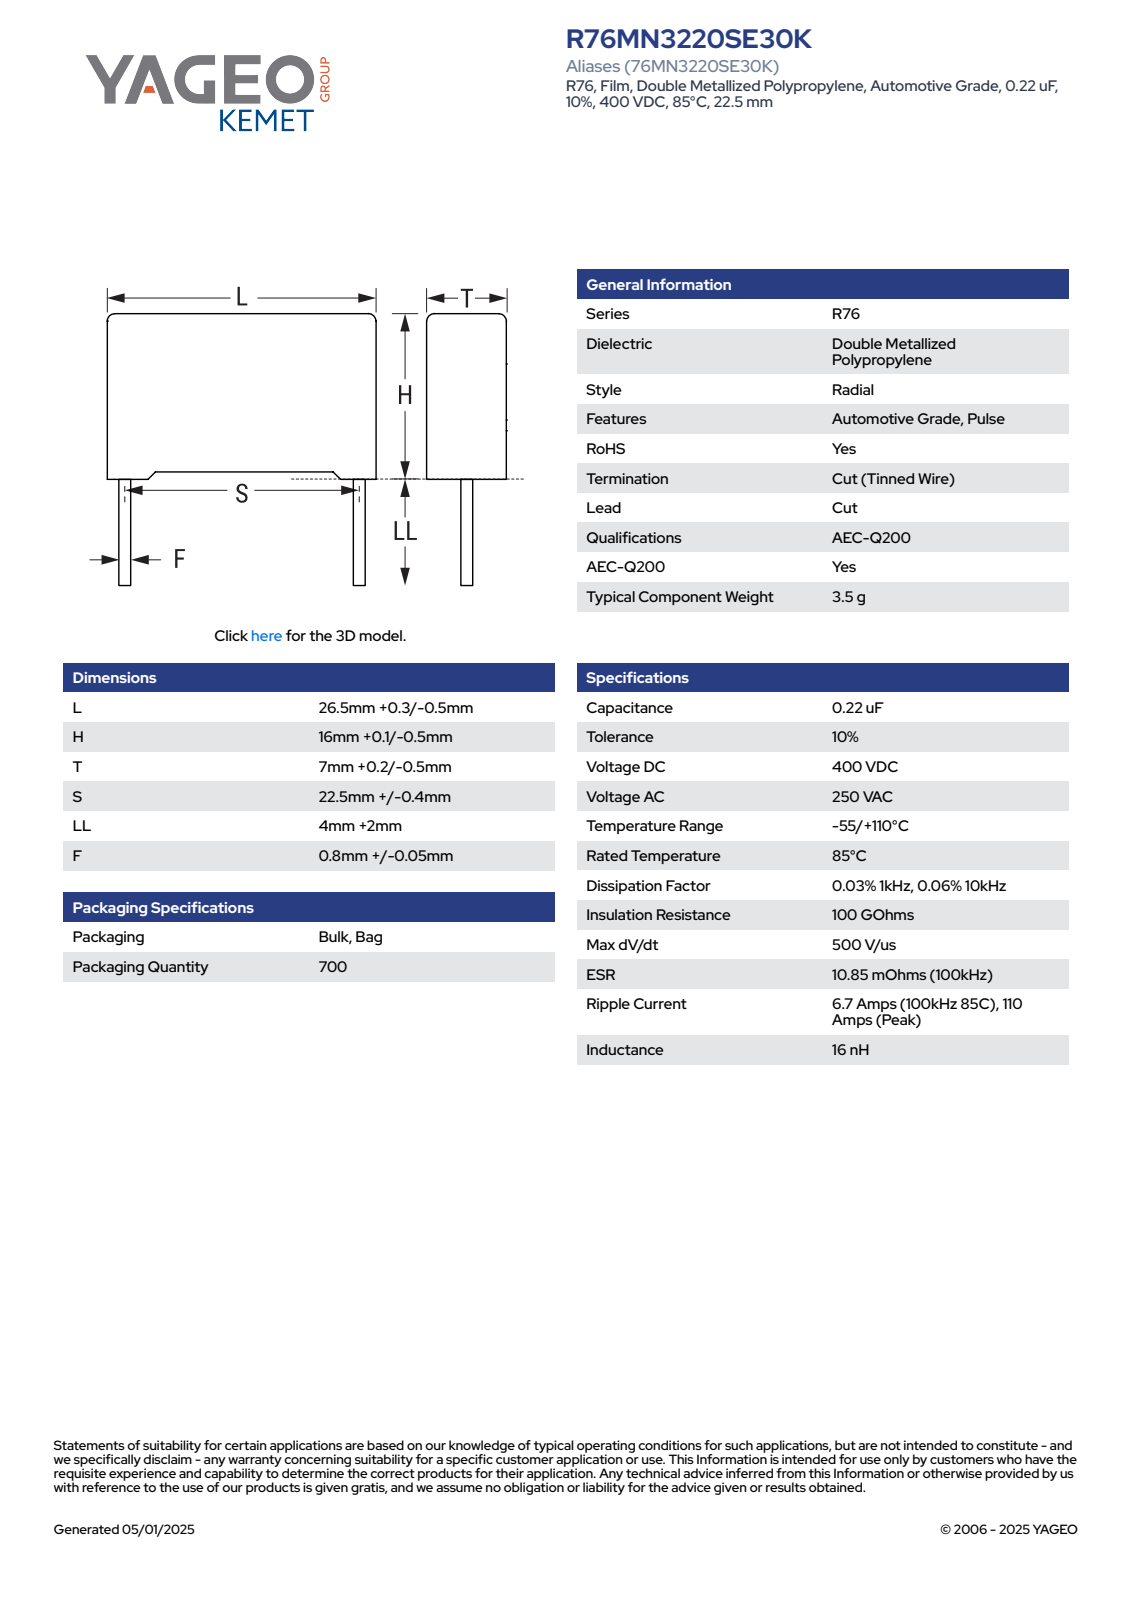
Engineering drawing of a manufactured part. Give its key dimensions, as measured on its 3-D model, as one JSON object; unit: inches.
{"part_name": "CFR_RB2_26.5X16X7_L26.8H16.1T7.2S22.5LL6F0.85", "step_written_by": "SolidWorks 2021 (AUTOMOTIVE_DESIGN)", "units": "inches", "bodies": {"solids": 4, "faces": 85, "planar": 77, "cylindrical": 8, "other": 0}, "overall_size": [1.055, 0.87, 0.284], "volume_in3": 0.183, "surface_area_in2": 2.42, "round_bosses_or_shafts": [[0.033, 2]], "partial_cylinders_radius": [[0.02, 4]], "face_to_face_distances": [0.283, 0.604, 1.055, 0.612, 0.035, 0.022, 0.03, 0.634, 0.248, 0.213]}
